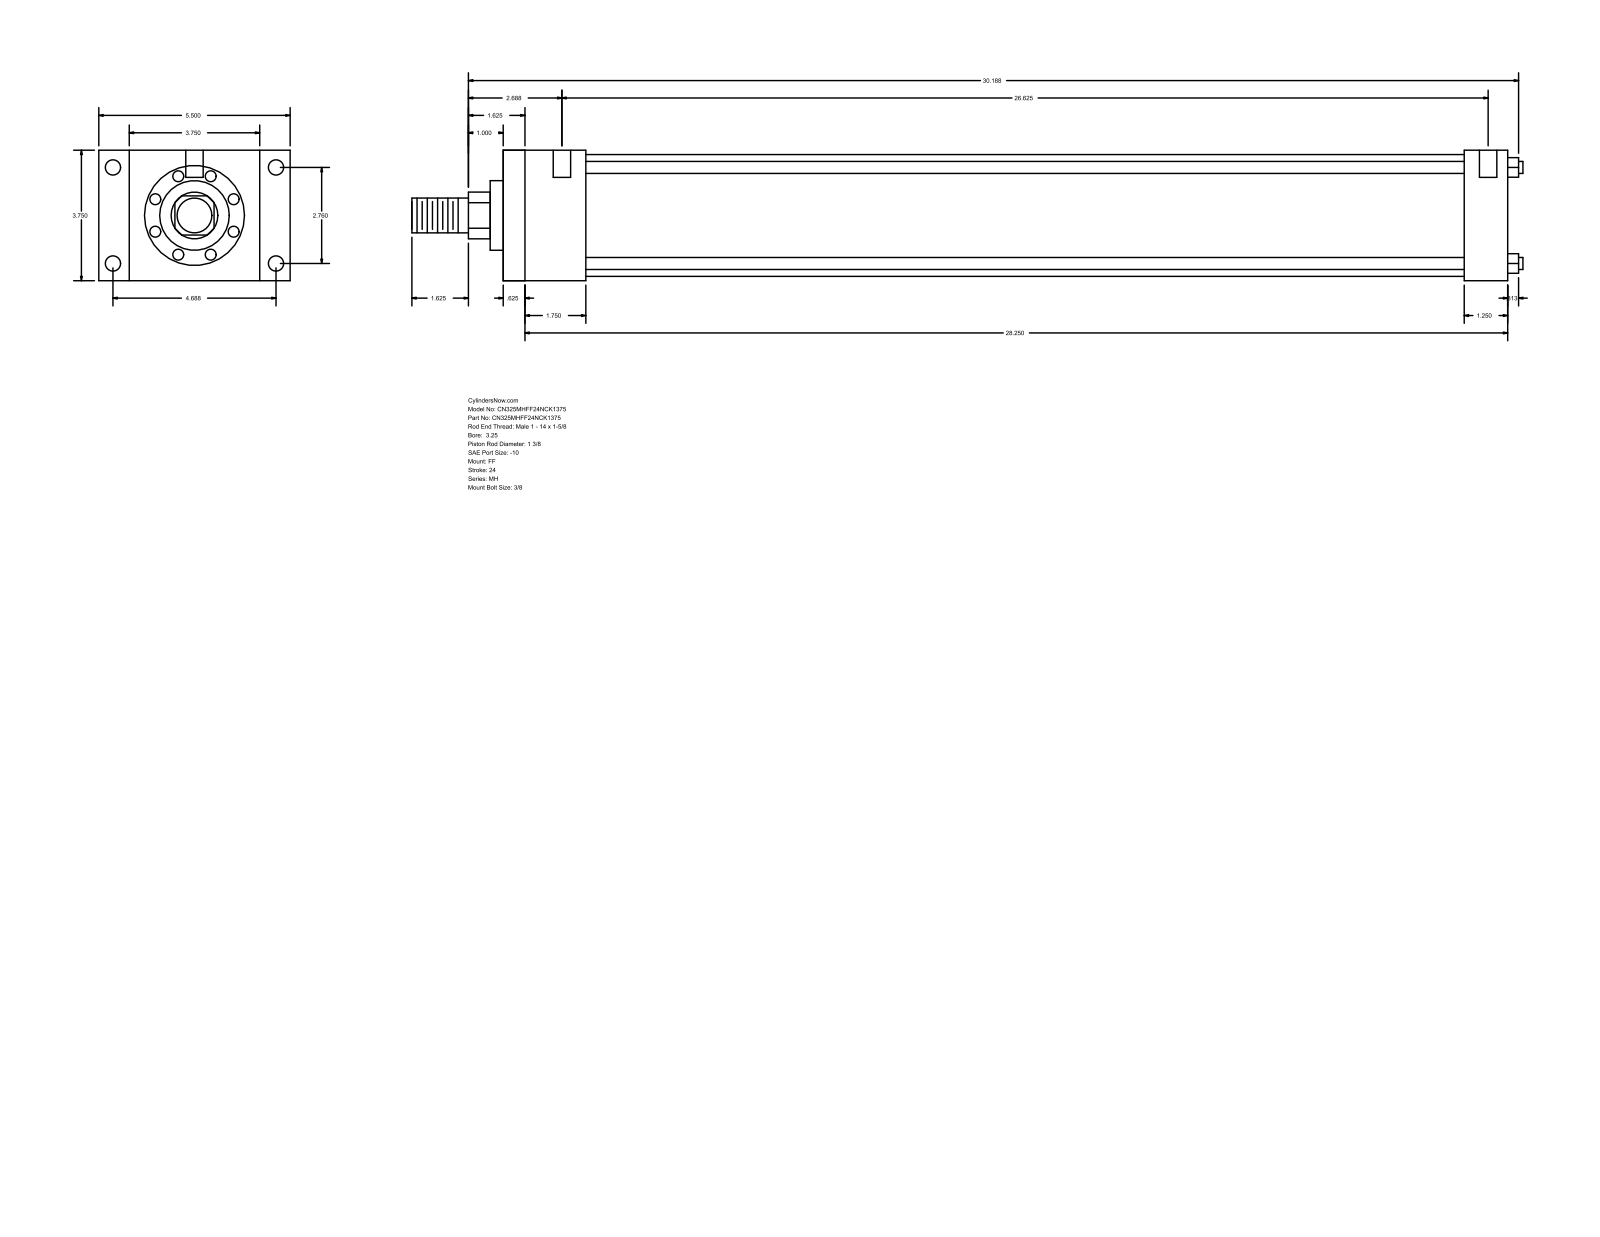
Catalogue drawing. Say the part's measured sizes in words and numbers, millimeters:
The part is named "MH_FF__0325_1.375". Its 3-D file was written by "GSSL Pune (CONFIG_CONTROL_DESIGN)". It is 0 solids with 92 faces: 64 planar, 28 cylindrical and 0 other. Overall it measures 811.21 by 139.7 by 95.25 millimeters. Round holes: 4 of diameter 5.56, 4 of diameter 11.13, 2 of diameter 12.7. Round bosses or shafts: 4 of diameter 8.76, 1 of diameter 88.9, 1 of diameter 50.8, 1 of diameter 34.92, 1 of diameter 25.4. Partial cylindrical surfaces (rounded edges, fillets, slot ends): 1 of radius 17.06. The main face-to-face distances are 95.24, 733.43, 15.87, 717.56, 22.23, 117.47, 701.68, 685.81, 31.75, 60.32. The hole center spacings are 70.1, 119.06, 138.16, 682.63, 1.59, 4.76, 676.28, 677.87.
